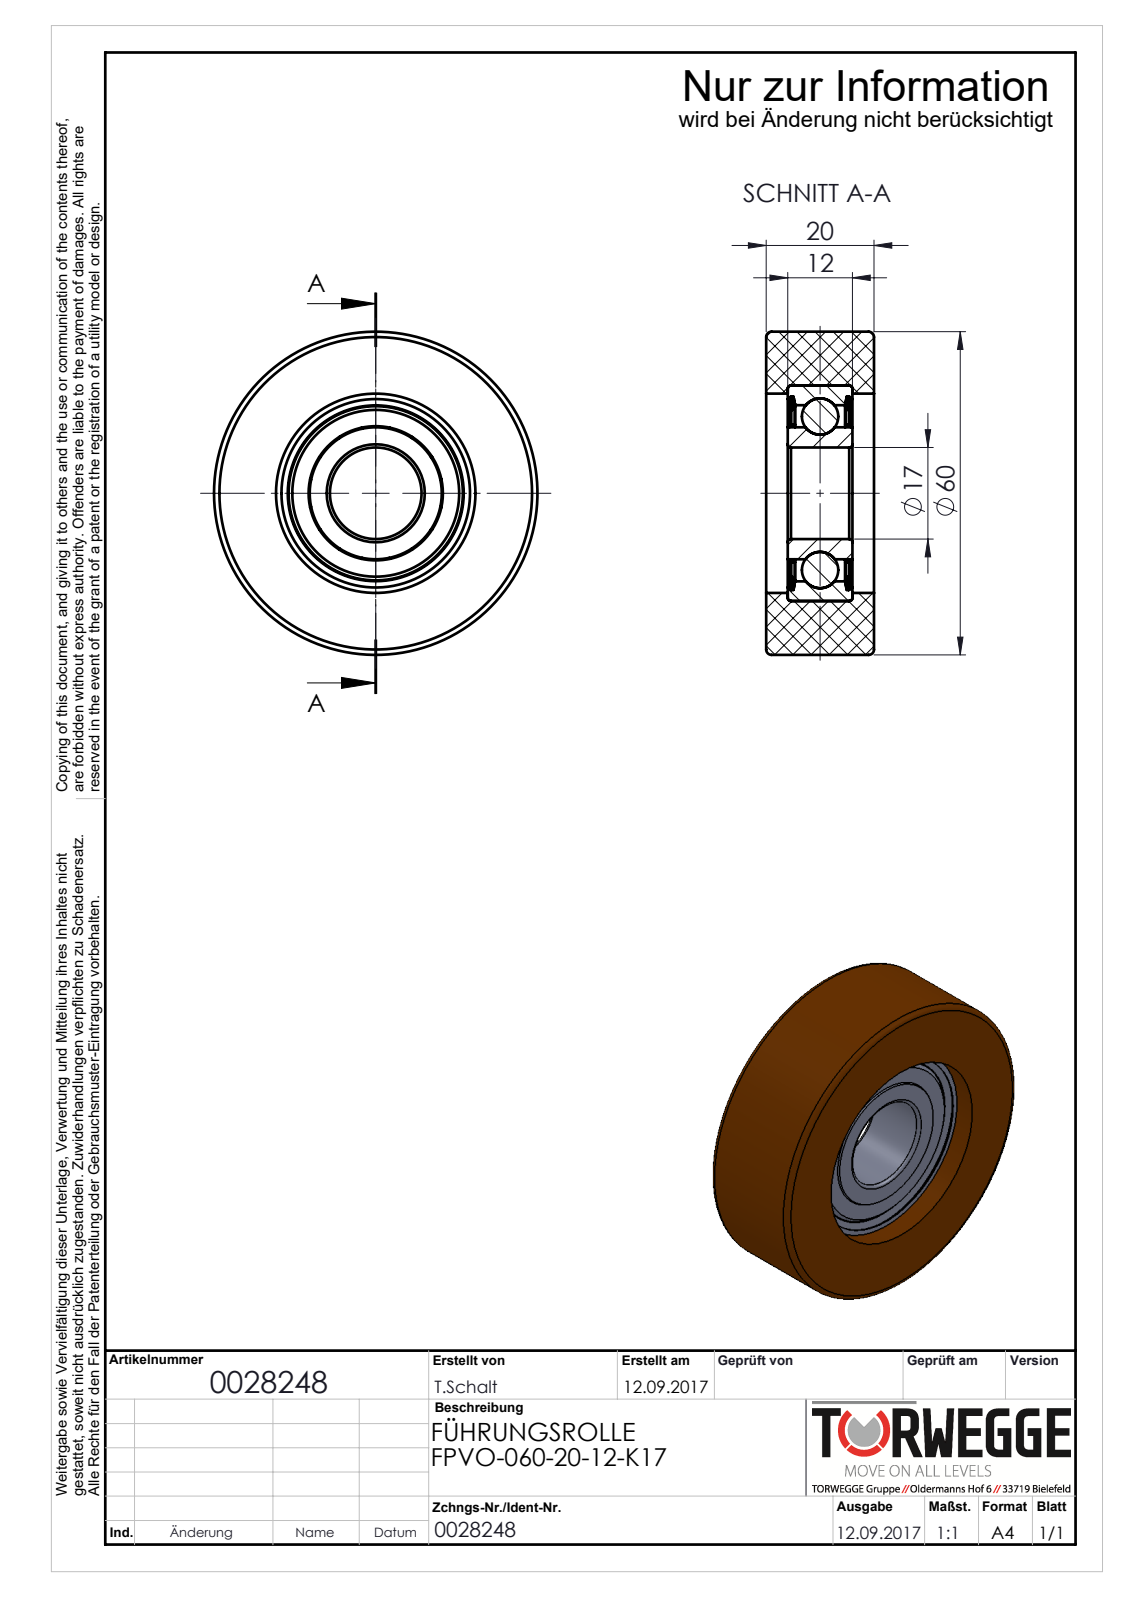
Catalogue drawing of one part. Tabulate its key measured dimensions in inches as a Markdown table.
| quantity | value |
| --- | --- |
| part name | roulement_6203-2z_2_1; 6203 ZZ; roulement_6203-2z_2_4; roulement_6203-2z_2_3 (+4 more) |
| STEP written by | SolidWorks 2016 (AUTOMOTIVE_DESIGN) |
| units | inches |
| bodies | 6 solids, 136 faces (18 planar, 36 cylindrical, 82 other) |
| overall size | 2.362 × 2.362 × 0.787 |
| volume | 2.512 in³ |
| surface area | 29.98 in² |
| round holes (diameter × count) | 0.669 × 1, 0.981 × 1, 1.287 × 1, 1.377 × 1, 1.457 × 1, 1.575 × 1 |
| round bosses / shafts (diameter × count) | 2.362 × 1, 1.413 × 1, 1.007 × 1, 0.965 × 1 |
| main face-to-face distances | 0.787, 0.157, 0.63, 0.472, 0.013, 0.434, 0.17, 0.013, 0.46, 0.617 |
